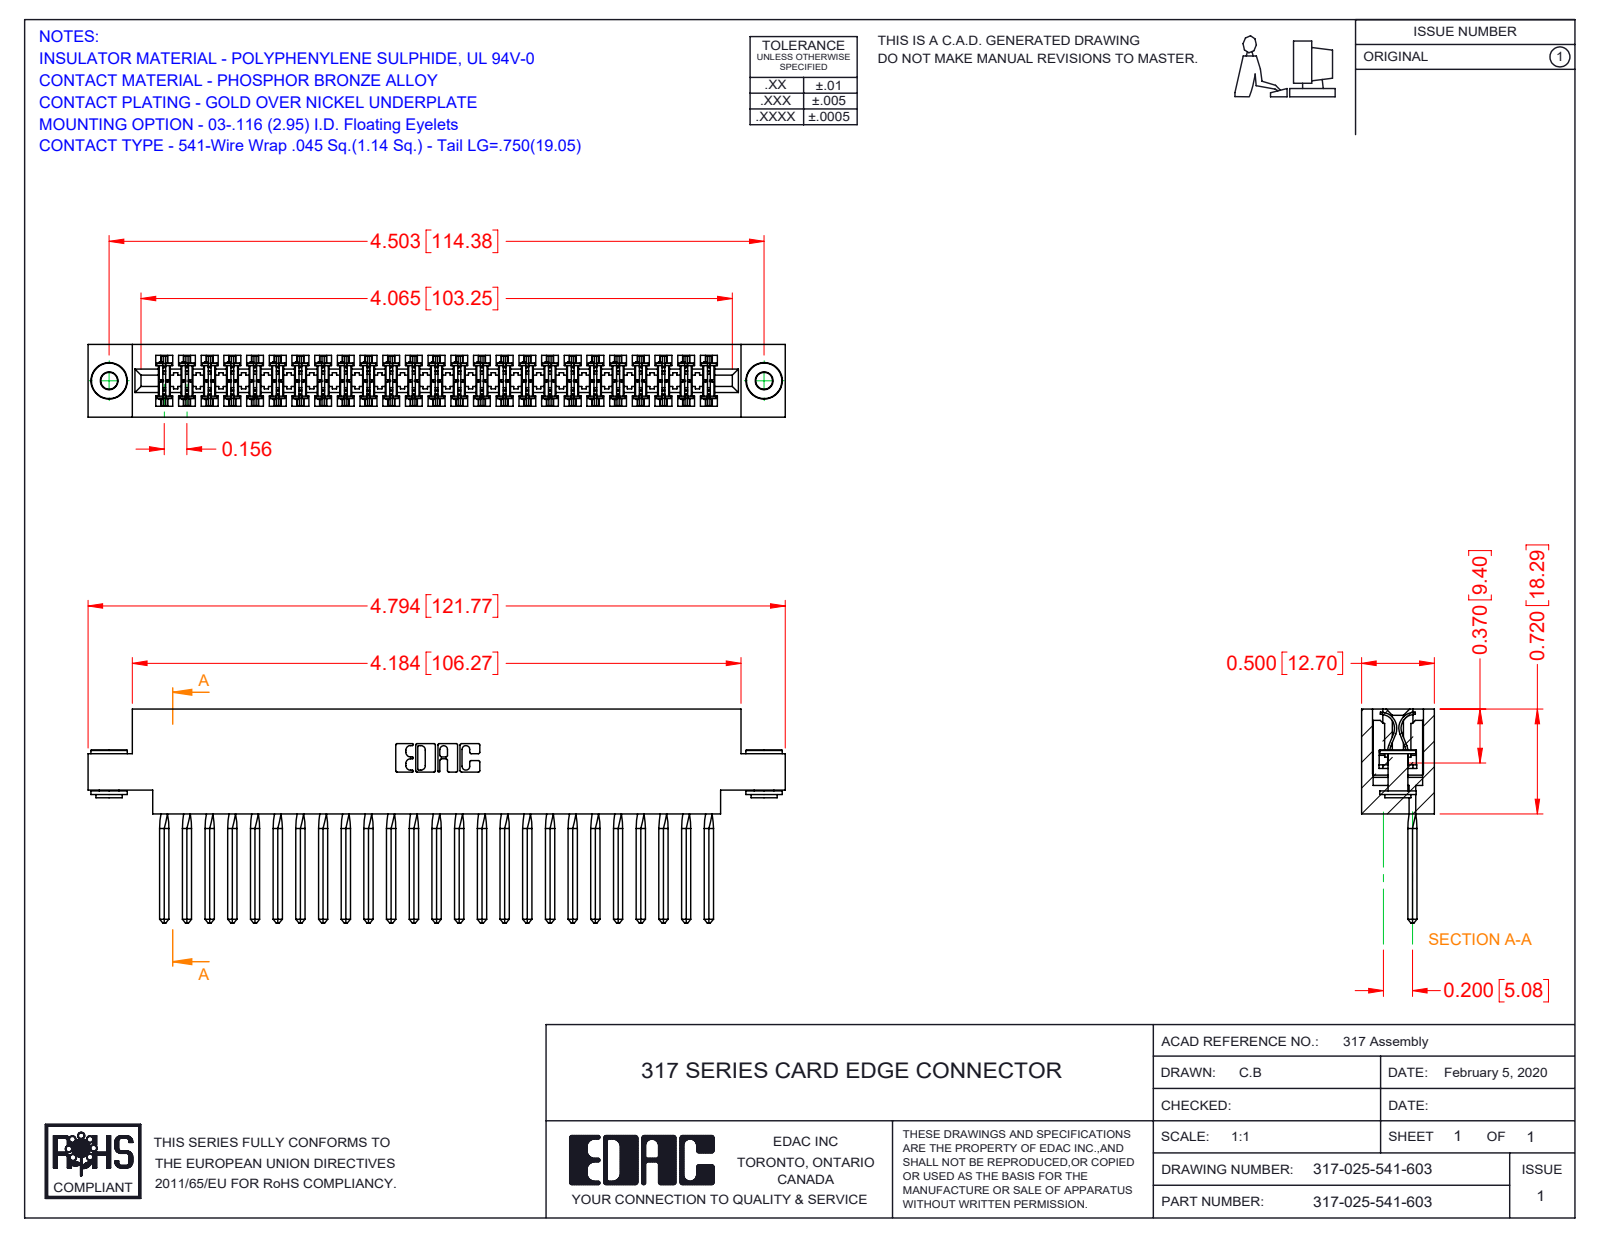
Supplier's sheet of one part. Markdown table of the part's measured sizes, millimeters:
| quantity | value |
| --- | --- |
| part name | 317-290-002_541; 317 Part_.156 Dia - TH; 317-025-541-603; 345-250-002_345-250-002-102 |
| STEP written by | SolidWorks 2016 (CONFIG_CONTROL_DESIGN) |
| units | millimeters |
| bodies | 28 solids, 3940 faces (3168 planar, 664 cylindrical, 108 other) |
| overall size | 121.8 × 37.3 × 12.7 |
| volume | 19 240 mm³ |
| surface area | 26 840 mm² |
| round holes (diameter × count) | 2.9 × 2, 4 × 2 |
| round bosses / shafts (diameter × count) | 6.4 × 2, 4.6 × 2, 3.5 × 2 |
| partial cylindrical surfaces (radius × count) | 0.4 × 50, 0.3 × 22, 0.2 × 6, 0.8 × 6, 0.7 × 3, 2.4 × 2, 2.5 × 2, 2.8 × 2 |
| main face-to-face distances | 12.7, 1.9, 10.8, 8.9, 2.8, 5, 18.3, 19.6, 5.6, 5.4 |
| hole center spacings | 114.4 |
